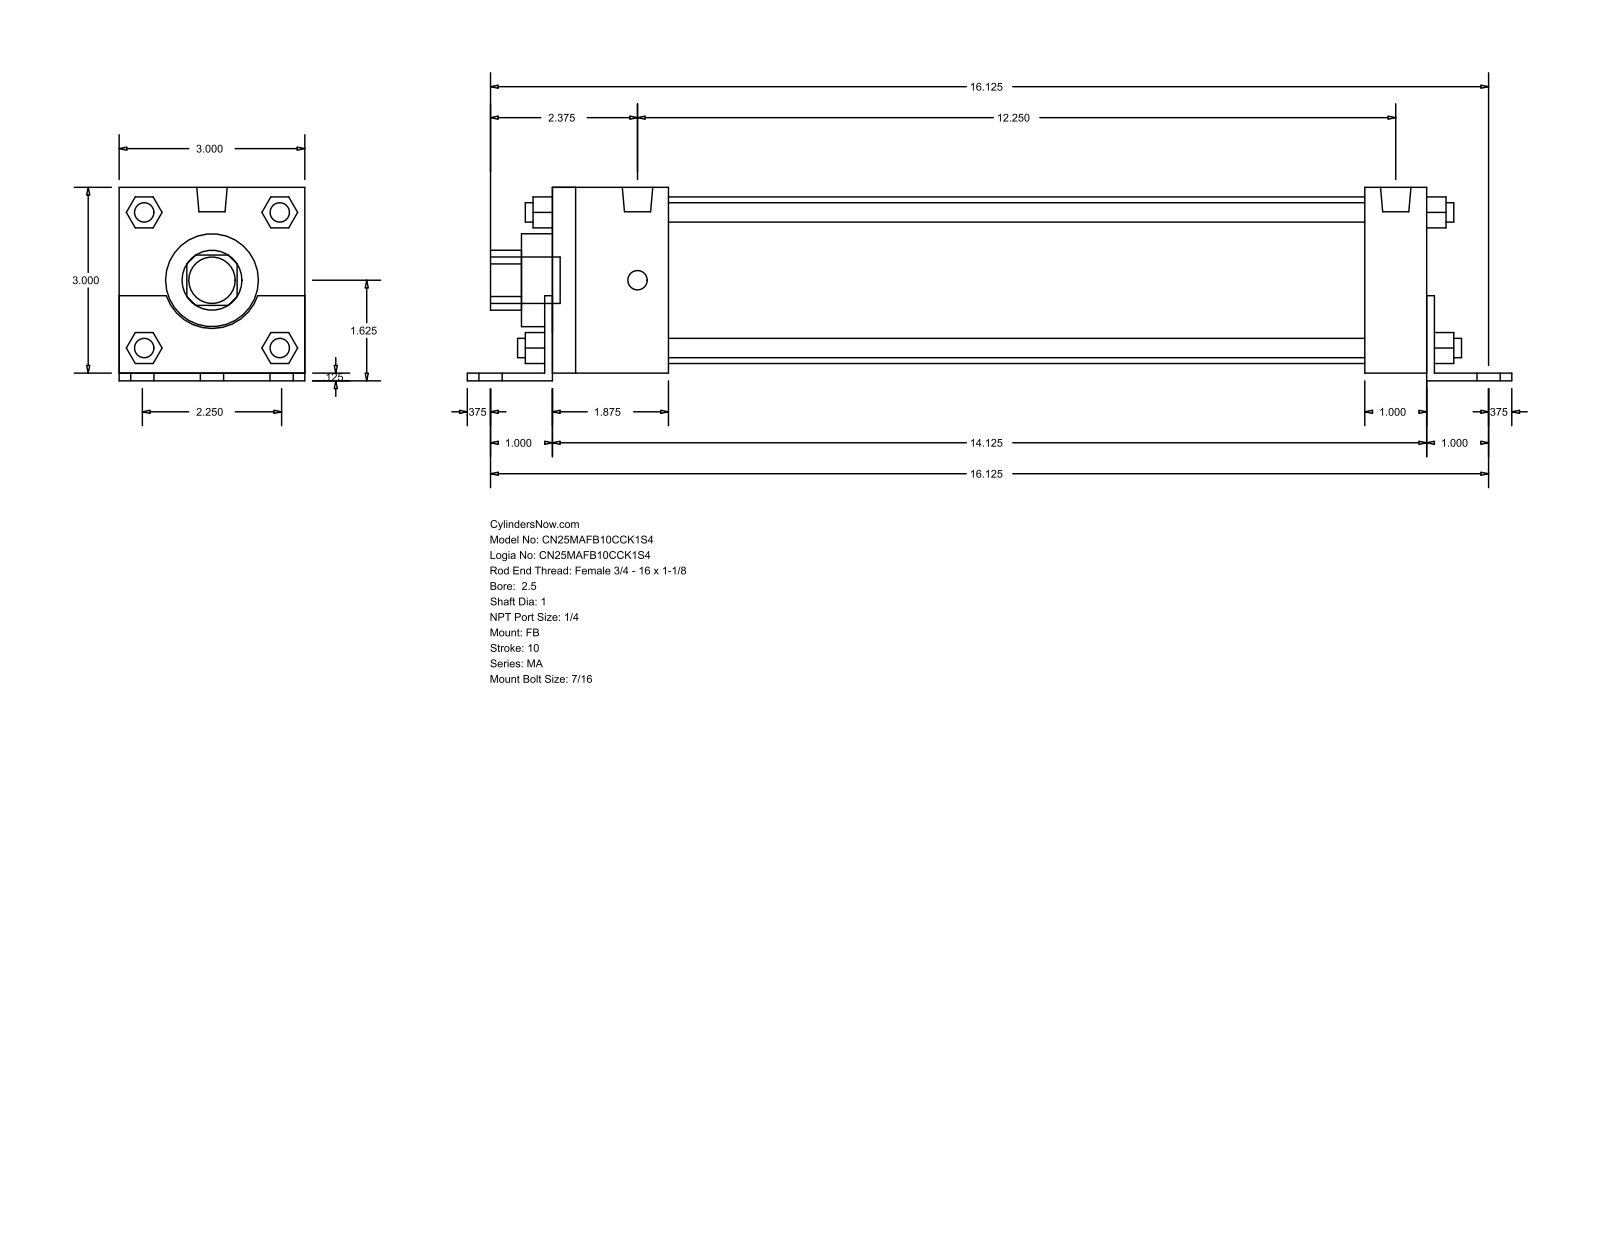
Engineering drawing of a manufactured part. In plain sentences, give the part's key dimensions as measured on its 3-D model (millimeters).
The part is named "MA_FB__0250_1". Its 3-D file was written by "GSSL Pune (CONFIG_CONTROL_DESIGN)". It is 0 solids with 140 faces: 105 planar, 35 cylindrical and 0 other. Overall it measures 428.62 by 79.38 by 76.2 millimeters. Round holes: 1 of diameter 25.4, 1 of diameter 38.1, 1 of diameter 68.33. Round bosses or shafts: 8 of diameter 7.94, 6 of diameter 11.11, 2 of diameter 12.49, 1 of diameter 19.05. Partial cylindrical surfaces (rounded edges, fillets, slot ends): 1 of radius 12.29, 1 of radius 19.81. The main face-to-face distances are 76.2, 3.17, 79.37, 361.95, 358.78, 12.7, 47.63, 311.15, 314.32, 333.37.
